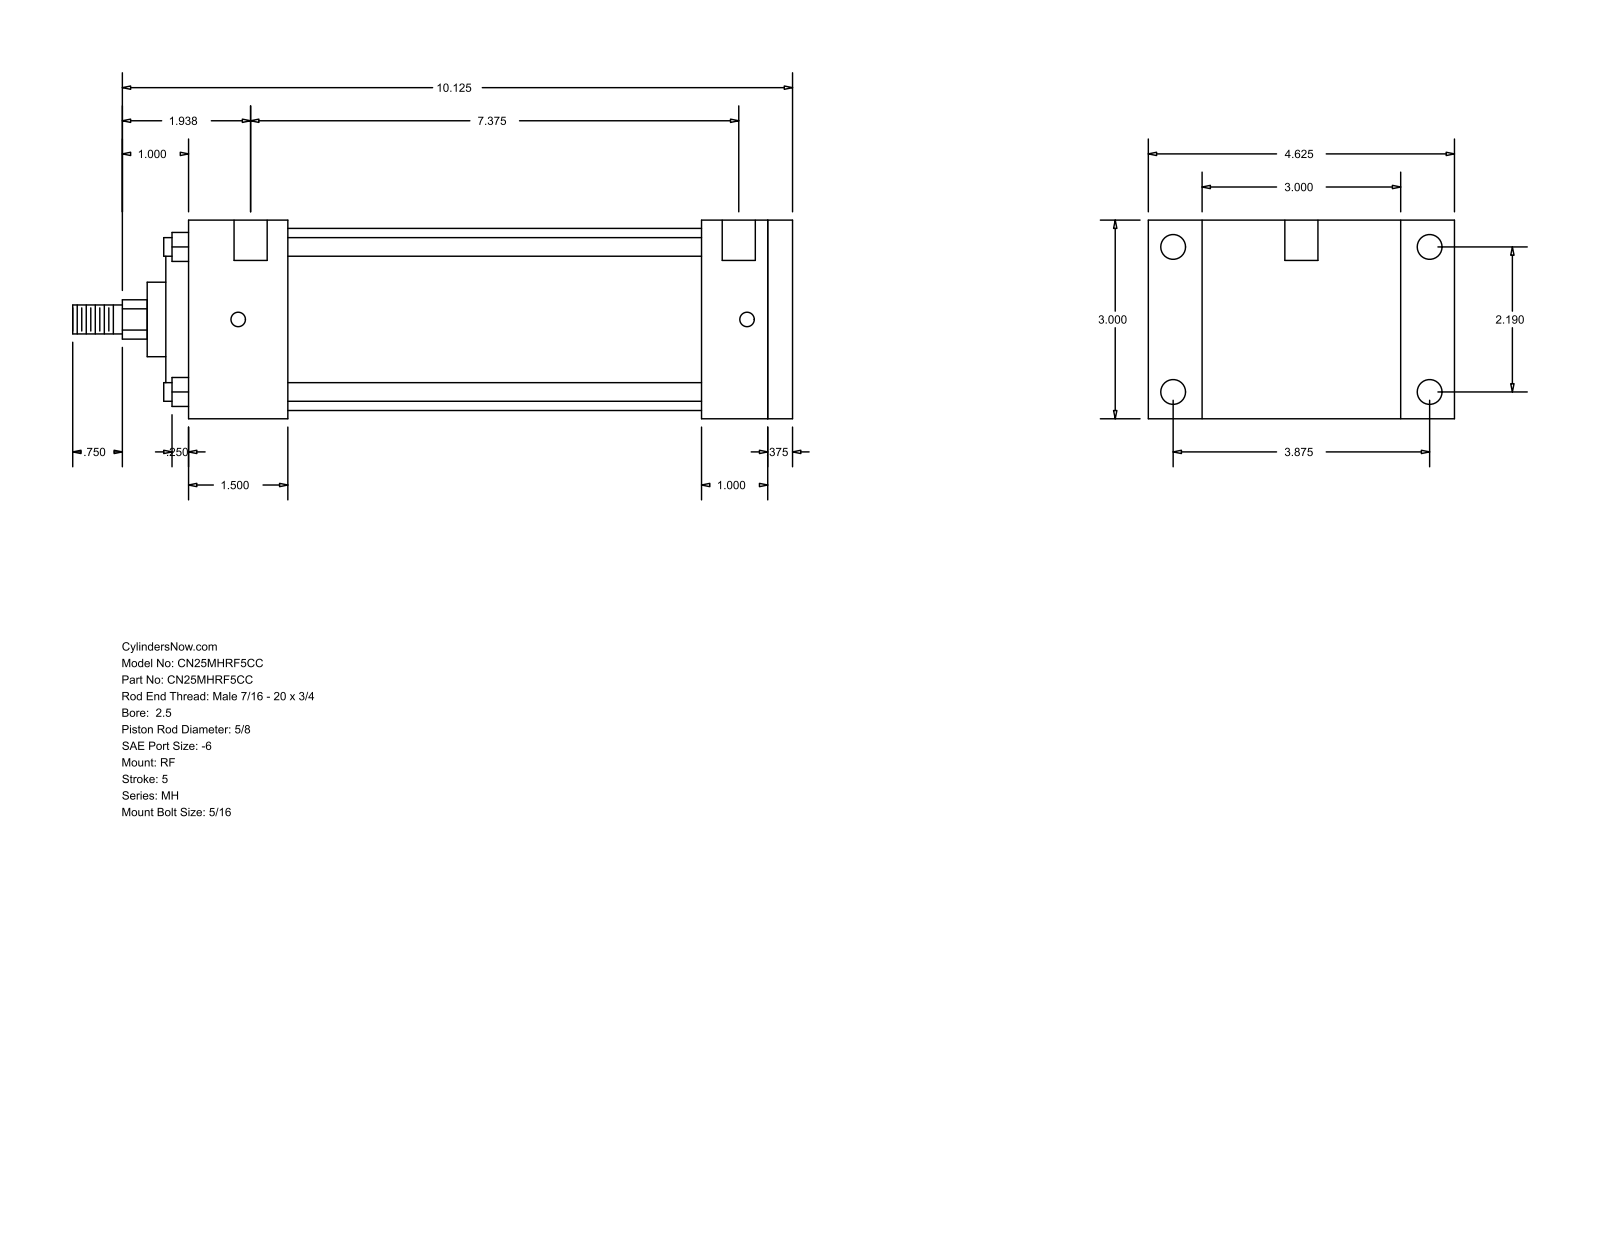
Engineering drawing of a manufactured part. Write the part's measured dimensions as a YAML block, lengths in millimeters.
part_name: "MH_RF__0250_0.625"
step_written_by: "GSSL Pune (CONFIG_CONTROL_DESIGN)"
units: millimeters
bodies: {solids: 0, faces: 94, planar: 65, cylindrical: 29, other: 0}
overall_size: [276.23, 117.47, 76.2]
round_holes:
  - {diameter: 5.56, count: 4}
  - {diameter: 9.53, count: 4}
  - {diameter: 12.7, count: 2}
round_bosses_or_shafts:
  - {diameter: 7.14, count: 4}
  - {diameter: 69.85, count: 1}
  - {diameter: 55.55, count: 1}
  - {diameter: 28.57, count: 1}
  - {diameter: 15.88, count: 1}
  - {diameter: 11.11, count: 1}
partial_cylinders:
  - {radius: 7.54, count: 1}
face_to_face_distances: [76.2, 9.53, 231.78, 222.25, 25.4, 34.93, 38.1, 196.85, 158.75, 184.15]
hole_center_spacings: [55.62, 98.42, 113.05, 195.26, 3.17, 4.76, 187.33, 190.5]
